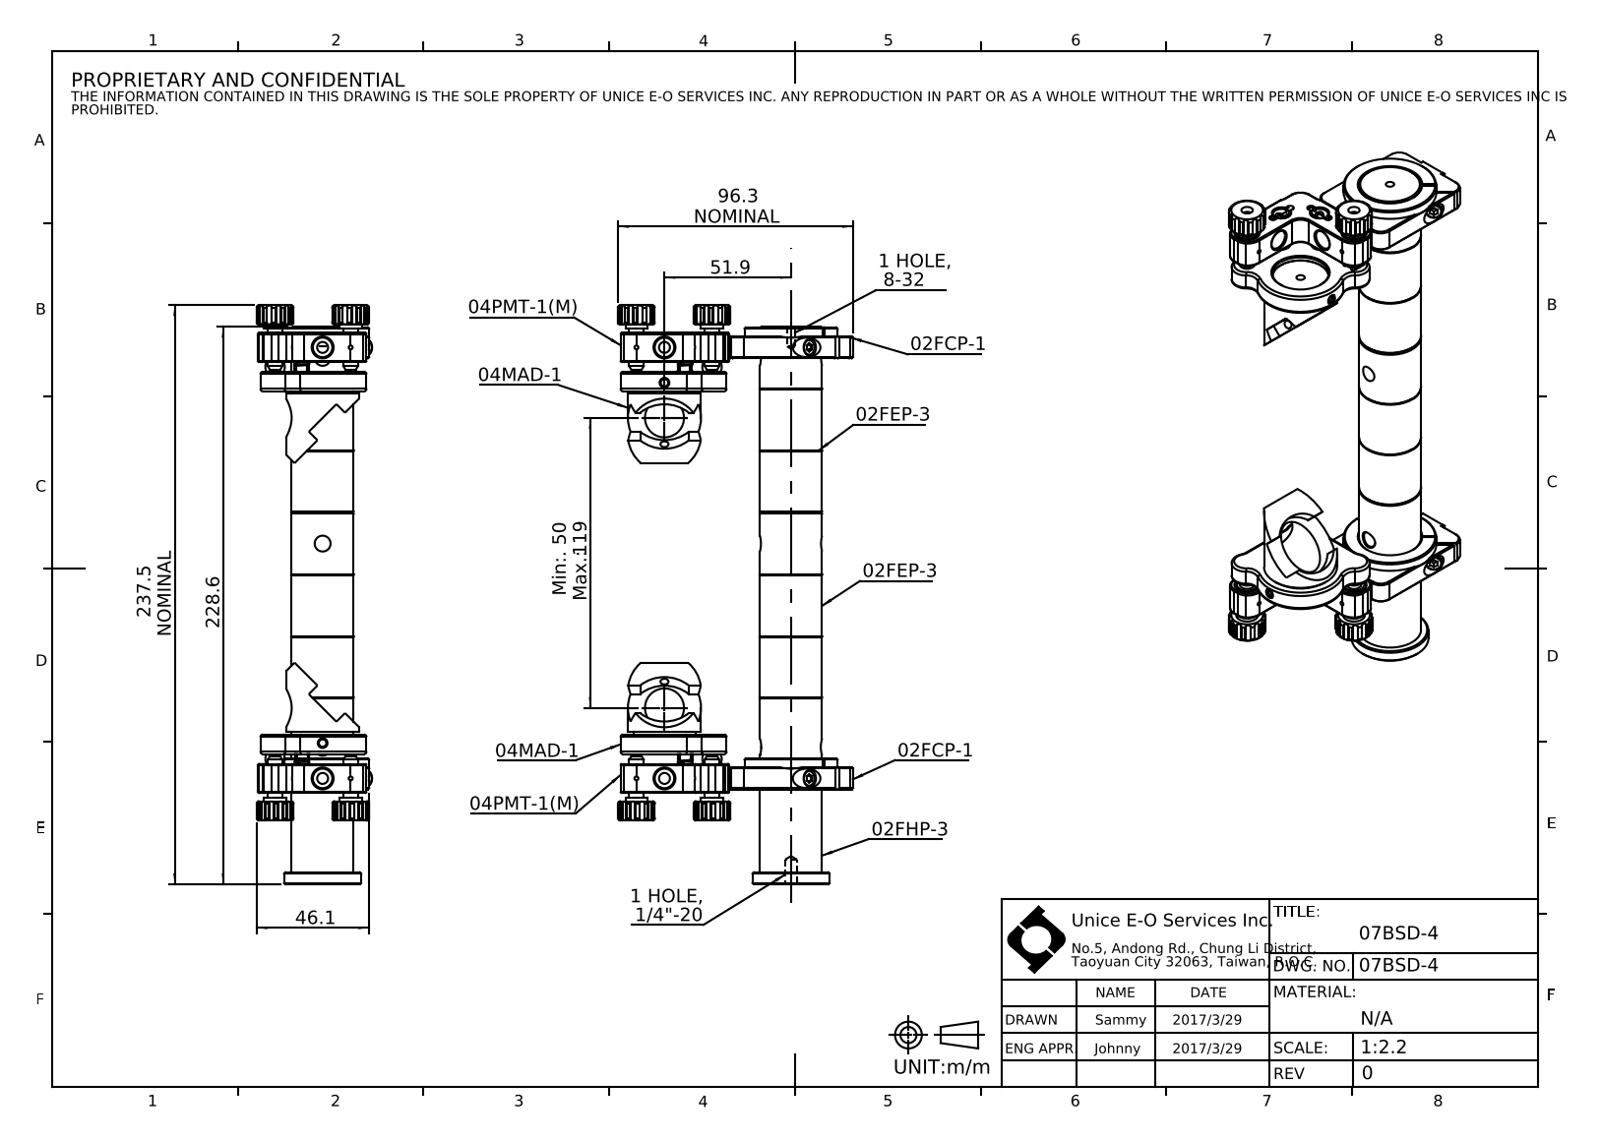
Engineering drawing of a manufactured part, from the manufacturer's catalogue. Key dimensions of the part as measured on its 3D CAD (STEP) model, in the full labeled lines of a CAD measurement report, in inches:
Part name (STEP PRODUCT): 07BSD-4
STEP written by: SolidWorks 2016 (CONFIG_CONTROL_DESIGN)
Units: inches
Bodies: 55 solids, 1629 faces (373 planar, 760 cylindrical, 496 other)
Overall size (bounding box): 9.352 × 3.791 × 1.862
Volume: 12.49 in³ · Surface area: 119.3 in²
Round holes (diameter × count): ⌀0.039 ×8, ⌀0.13 ×7, ⌀0.177 ×6, ⌀0.315 ×6, ⌀0.063 ×4, ⌀0.067 ×4, ⌀0.136 ×4, ⌀0.256 ×3, ⌀0.157 ×2, ⌀0.185 ×2, ⌀0.201 ×2, ⌀0.232 ×2
Round bosses / shafts (diameter × count): ⌀0.031 ×32, ⌀0.059 ×12, ⌀0.157 ×4, ⌀0.354 ×2, ⌀0.276 ×2, ⌀0.098 ×2, ⌀1.5 ×1, ⌀1.24 ×1
Partial cylindrical surfaces — rounded edges, fillets, slot ends (radius × count): R0.012 ×96, R0.059 ×50, R0.02 ×40, R0.197 ×23, R0.039 ×12, R0.098 ×9, R0.03 ×8, R0.236 ×3
Main face-to-face distances: 6.963, 0.315, 0.472, 0.059, 0.217, 6.077, 0.413, 6.491, 0.531, 5.861
Hole centre spacings: 6.963, 0.453, 0.679, 0.984, 6.381, 6.421, 6.978, 0.335
